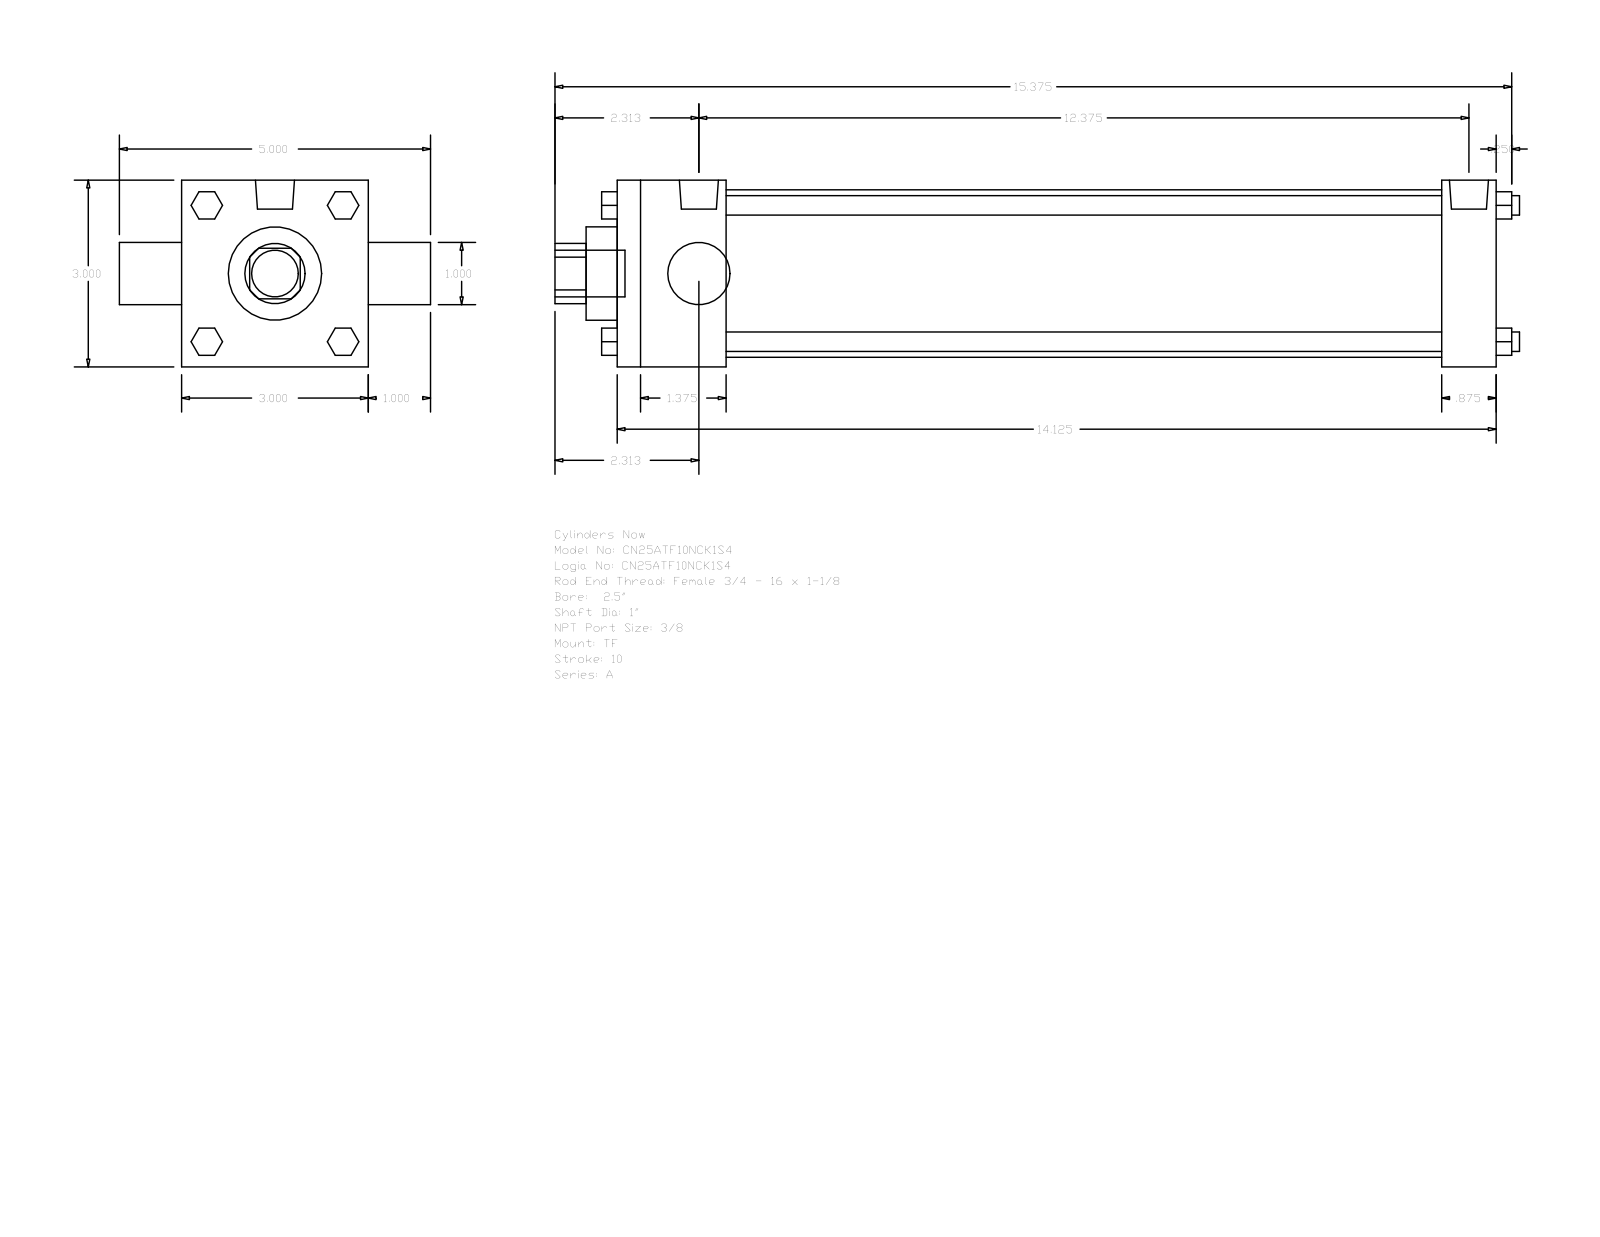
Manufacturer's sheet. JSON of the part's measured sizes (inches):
{"part_name": "A_TF__0250_1", "step_written_by": "GSSL Pune (CONFIG_CONTROL_DESIGN)", "units": "inches", "bodies": {"solids": 0, "faces": 120, "planar": 92, "cylindrical": 28, "other": 0}, "overall_size": [15.5, 5, 3], "round_holes": [[1, 2], [1.5, 1], [2.69, 1]], "round_bosses_or_shafts": [[0.313, 4], [0.219, 3], [0.627, 2], [0.75, 1]], "partial_cylinders_radius": [[0.484, 1]], "face_to_face_distances": [3, 14.125, 1.75, 13.25, 11.5, 12.375, 0.875, 1, 4, 0.5]}
